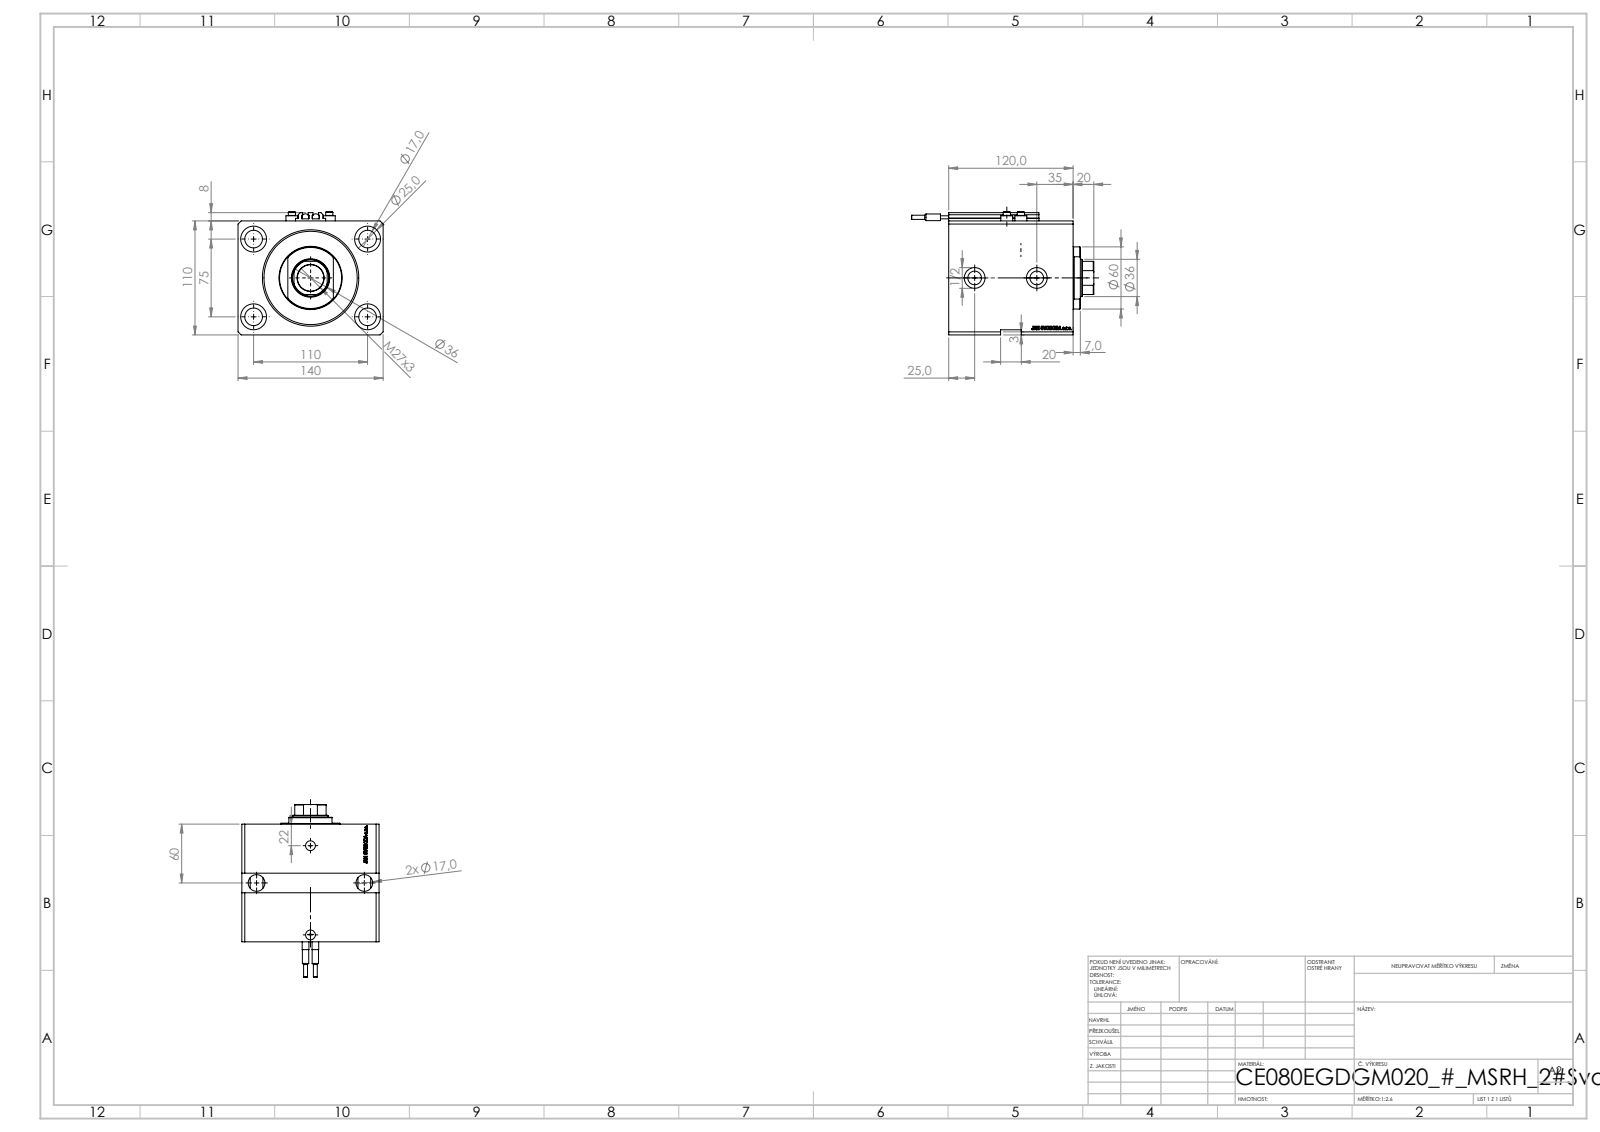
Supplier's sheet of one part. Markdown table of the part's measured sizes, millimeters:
| quantity | value |
| --- | --- |
| part name | ALLEN BOLT V250CE; V250CE_E_Body; V250CE_VC_E; SWITCH_V250CE (+1 more) |
| STEP written by | SolidWorks 2019 (CONFIG_CONTROL_DESIGN) |
| units | millimeters |
| bodies | 10 solids, 1181 faces (585 planar, 150 cylindrical, 446 other) |
| overall size | 176 × 140 × 119 |
| volume | 1 591 000 mm³ |
| surface area | 221 236 mm² |
| round holes (diameter × count) | 17 × 6, 1.25 × 4, 4 × 4, 25 × 4, 10 × 2, 13.16 × 2, 20 × 2, 25.5 × 1, 36 × 1, 80 × 1, 93 × 1 |
| round bosses / shafts (diameter × count) | 11.6 × 4, 7 × 4, 6.8 × 2, 6.5 × 2, 4 × 2, 60 × 1 |
| partial cylindrical surfaces (radius × count) | 0.2 × 10, 17.5 × 1 |
| main face-to-face distances | 110, 20, 140, 25, 95, 120, 100, 75, 40, 55 |
| hole center spacings | 66.57, 110, 13.6, 33.62, 36, 37.22, 38.23, 38.48 |
